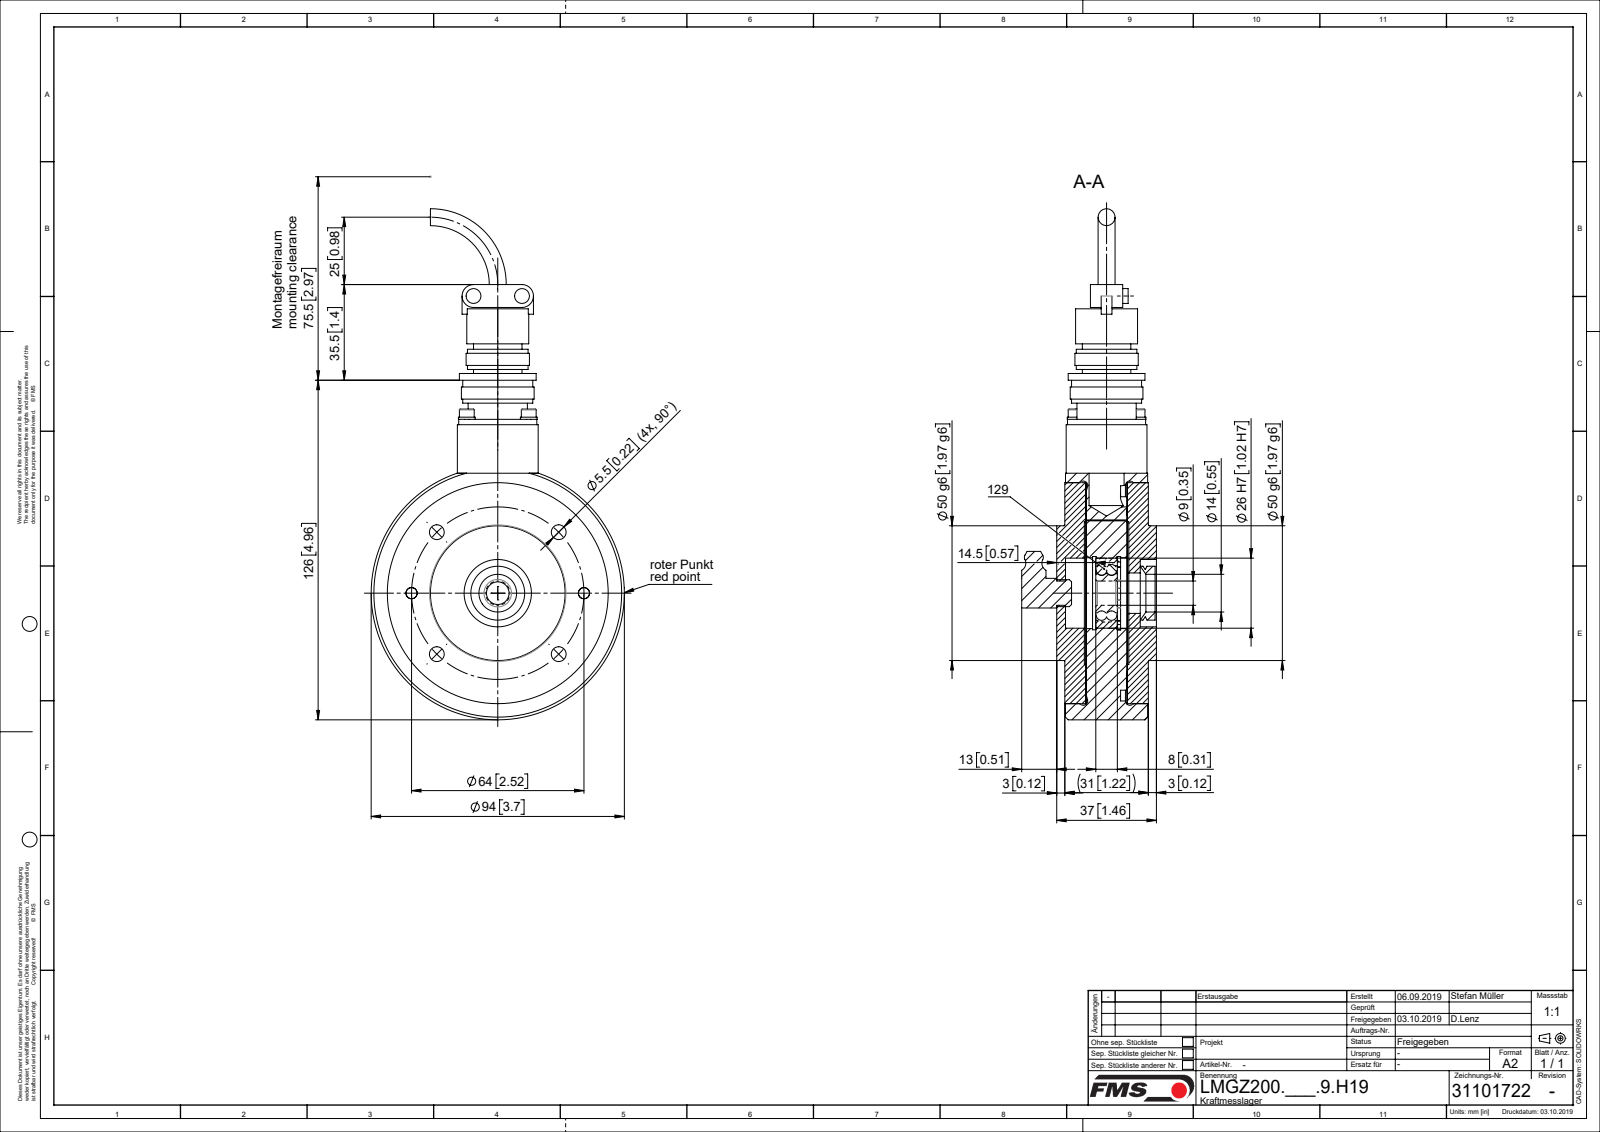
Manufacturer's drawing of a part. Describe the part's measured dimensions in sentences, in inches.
The part is named "L31101722; L4900504; L49966; TEIL1 (+8 more)". Its 3-D file was written by "Mechanical Desktop 2009 (CONFIG_CONTROL_DESIGN)". It is 21 solids with 425 faces: 126 planar, 243 cylindrical and 56 other. Overall it measures 7.467 by 3.701 by 2.028 inches. Its volume is 14.55 cubic inches and its surface area 140.8 square inches. Round holes: 6 of diameter 0.217, 4 of diameter 0.102, 4 of diameter 0.126, 4 of diameter 0.134, 4 of diameter 0.17, 4 of diameter 0.26, 2 of diameter 0.394, 1 of diameter 0.342, 1 of diameter 0.354, 1 of diameter 0.512, 1 of diameter 0.551, 1 of diameter 0.591. Round bosses or shafts: 6 of diameter 0.217, 4 of diameter 0.244, 4 of diameter 0.118, 4 of diameter 0.098, 3 of diameter 0.315, 2 of diameter 0.197, 1 of diameter 3.701, 1 of diameter 3.228. Partial cylindrical surfaces (rounded edges, fillets, slot ends): 2 of radius 0.167, 2 of radius 0.315, 1 of radius 0.157. The main face-to-face distances are 0.6, 0.915, 0.315, 0.906, 0.305, 0.591, 0.61, 0.02, 0.285, 0.433. The hole center spacings are 1.26, 0.64, 0.906, 0.964, 1.782, 2.328, 2.471, 0.491.
